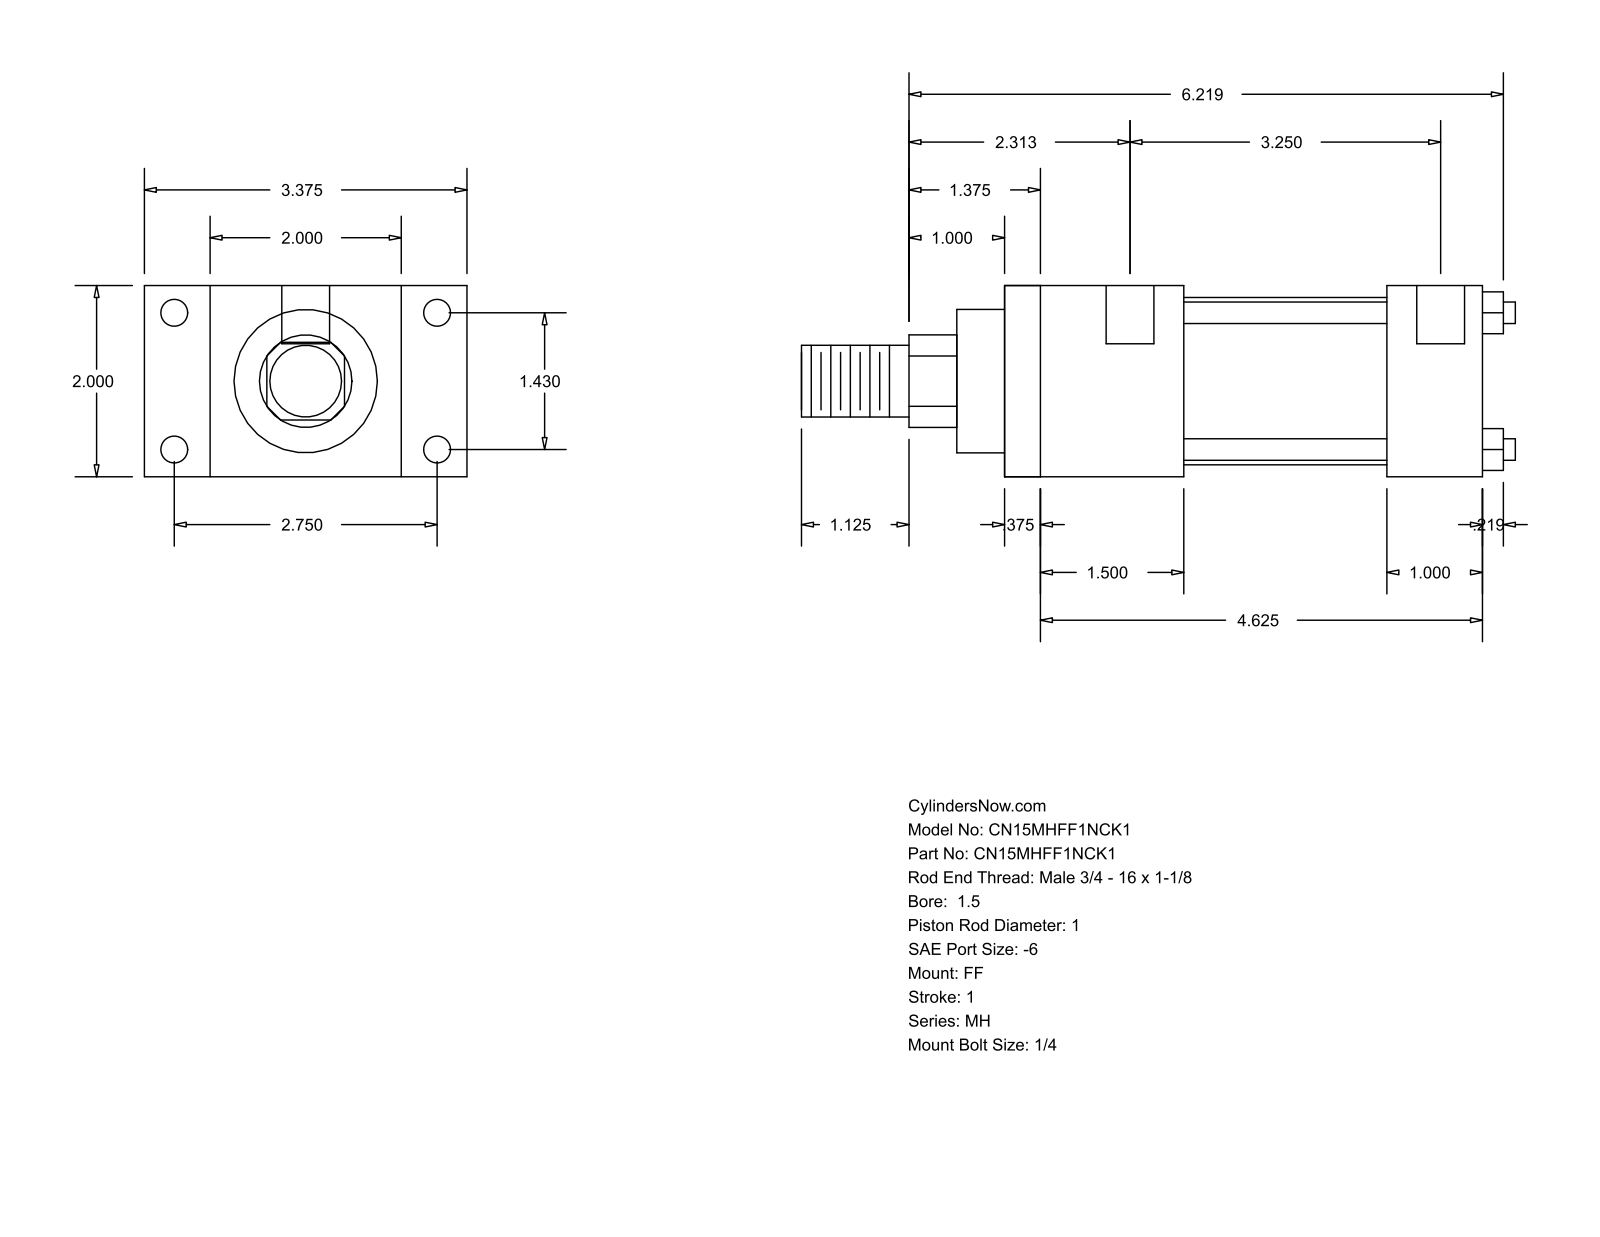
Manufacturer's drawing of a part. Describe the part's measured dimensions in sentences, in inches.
The part is named "MH_FF__0150_1". Its 3-D file was written by "GSSL Pune (CONFIG_CONTROL_DESIGN)". It is 0 solids with 92 faces: 64 planar, 28 cylindrical and 0 other. Overall it measures 7.469 by 3.375 by 2 inches. Round holes: 4 of diameter 0.219, 4 of diameter 0.281, 2 of diameter 0.5. Round bosses or shafts: 4 of diameter 0.225, 1 of diameter 1.75, 1 of diameter 1.5, 1 of diameter 1, 1 of diameter 0.75. Partial cylindrical surfaces (rounded edges, fillets, slot ends): 1 of radius 0.484. The main face-to-face distances are 2, 5, 0.375, 4.625, 2.125, 4, 1, 0.687, 2.687, 1.875. The hole center spacings are 1.43, 2.75, 3.099, 3.375, 0.125, 3.25.
